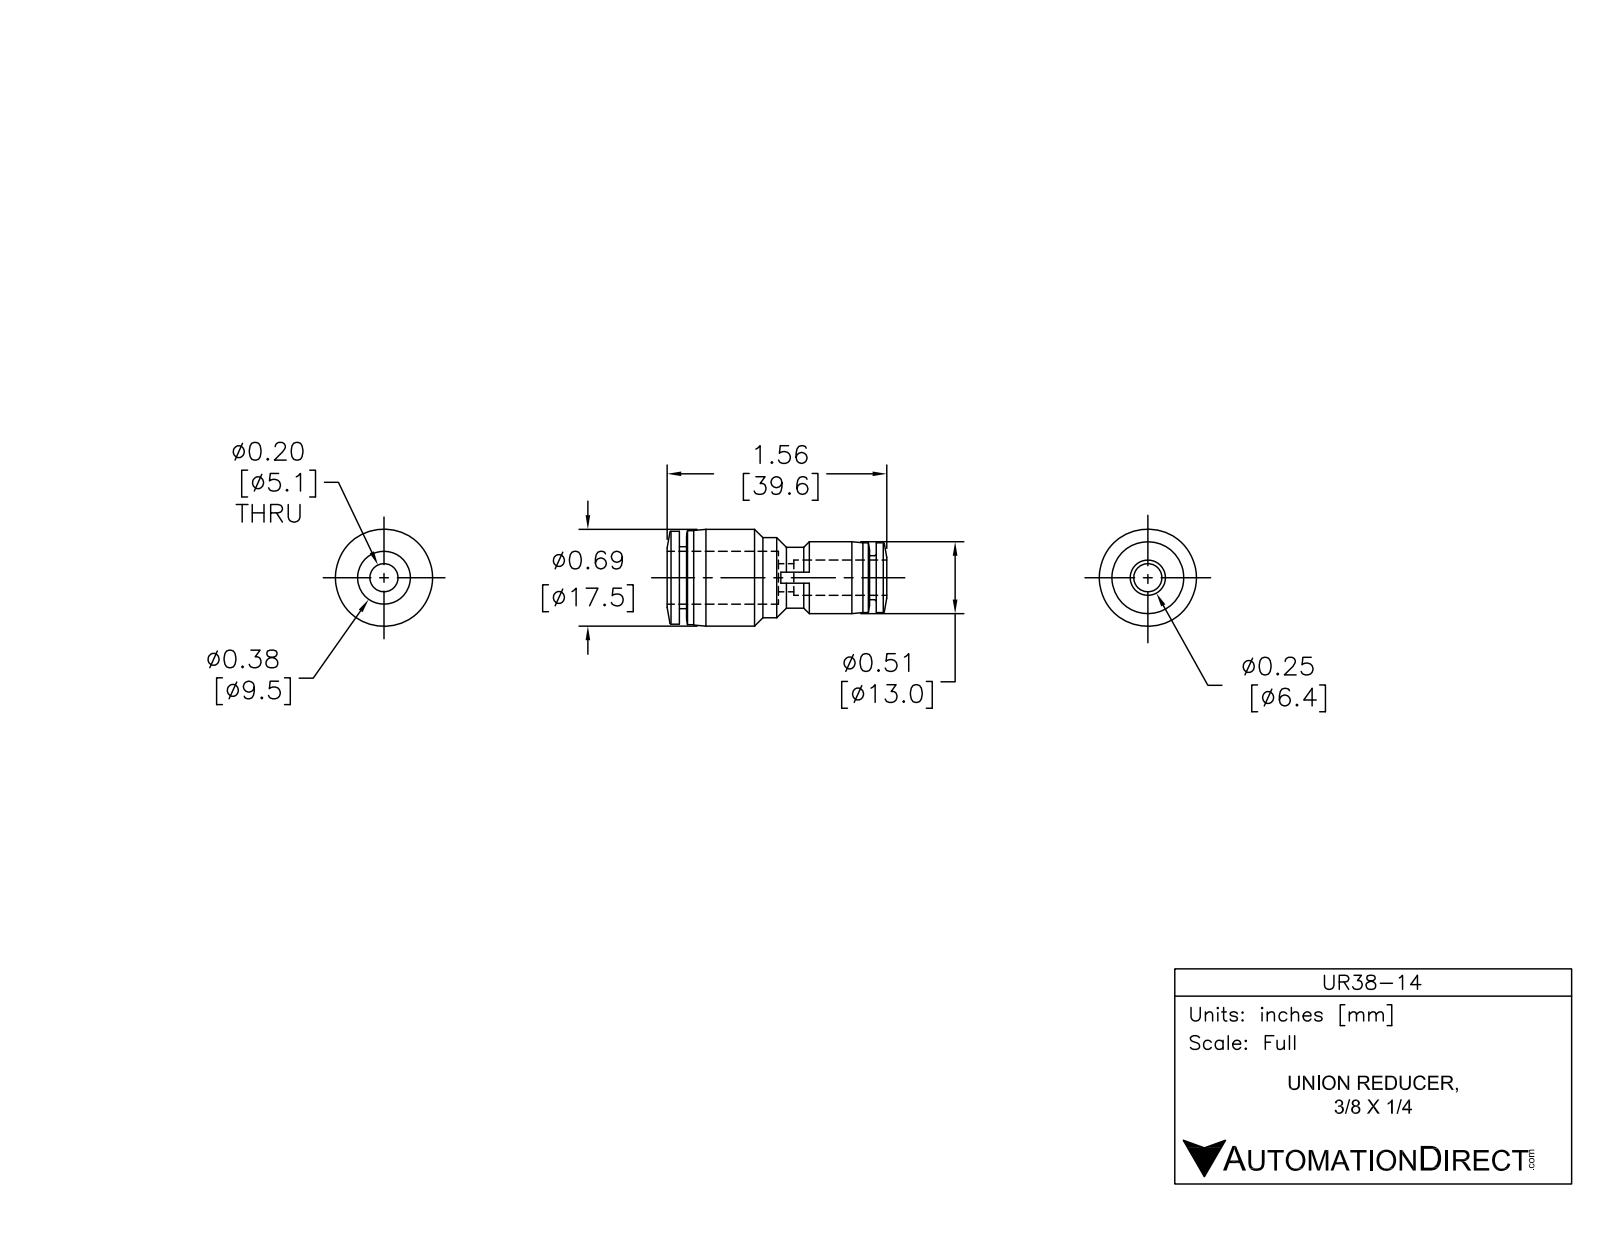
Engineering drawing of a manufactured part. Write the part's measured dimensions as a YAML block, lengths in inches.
part_name: "UR38-14"
step_written_by: "SolidWorks 2015 (AUTOMOTIVE_DESIGN)"
units: inches
bodies: {solids: 1, faces: 71, planar: 11, cylindrical: 27, other: 33}
overall_size: [1.563, 0.689, 0.689]
volume: 0.27
surface_area: 5.453
round_holes:
  - {diameter: 0.197, count: 1}
  - {diameter: 0.258, count: 1}
  - {diameter: 0.386, count: 1}
round_bosses_or_shafts:
  - {diameter: 0.689, count: 1}
  - {diameter: 0.669, count: 1}
  - {diameter: 0.661, count: 1}
  - {diameter: 0.571, count: 1}
  - {diameter: 0.512, count: 1}
  - {diameter: 0.496, count: 1}
  - {diameter: 0.441, count: 1}
  - {diameter: 0.433, count: 1}
face_to_face_distances: [0.051, 1.35, 1.402, 0.697, 0.654, 0.705, 0.047, 0.65, 1.303, 1.354]
